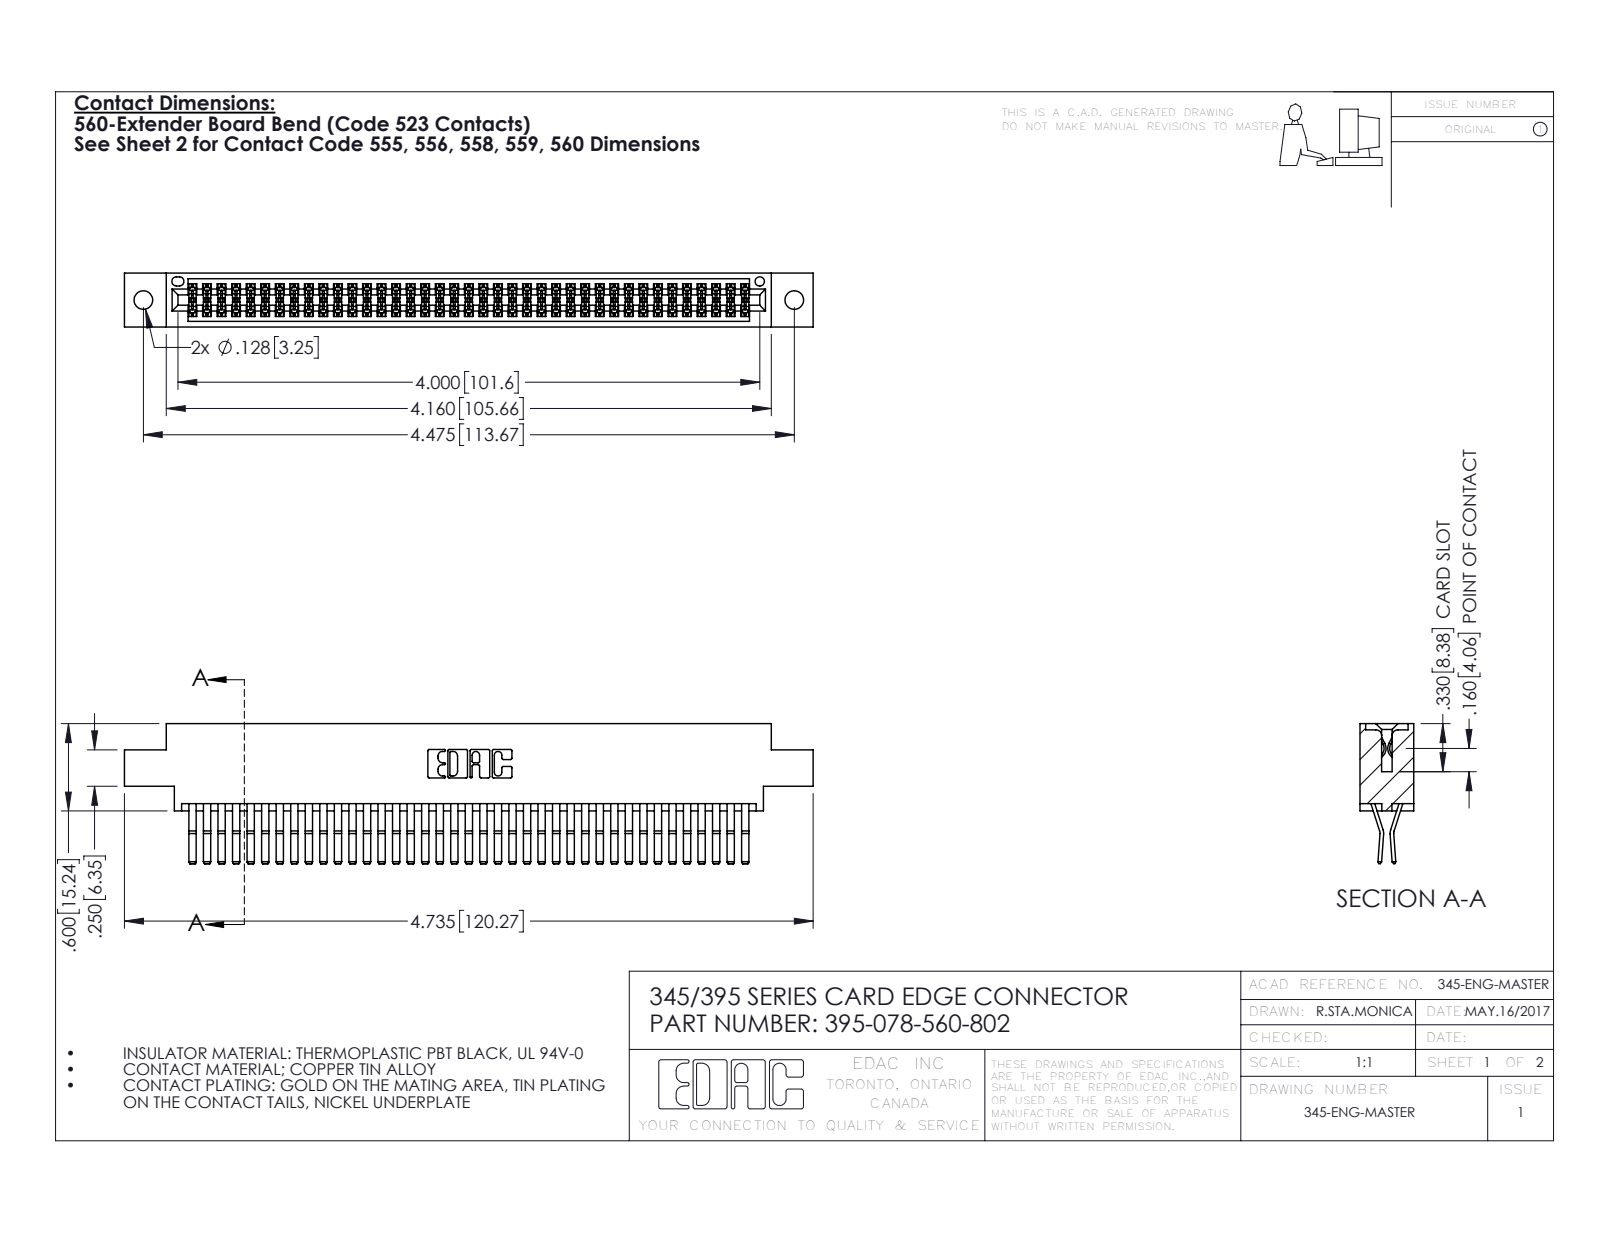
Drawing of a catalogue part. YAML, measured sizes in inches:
part_name: "345-292-001_560 Tail; 345 Part_0.170 Offset - 0.128 Dia; 395-078-560-802"
step_written_by: "SolidWorks 2016 (CONFIG_CONTROL_DESIGN)"
units: inches
bodies: {solids: 79, faces: 4186, planar: 2658, cylindrical: 1528, other: 0}
overall_size: [4.735, 0.962, 0.37]
volume: 0.733
surface_area: 29.28
round_holes:
  - {diameter: 0.128, count: 2}
  - {diameter: 0.064, count: 1}
partial_cylinders:
  - {radius: 0.006, count: 117}
  - {radius: 0.01, count: 22}
  - {radius: 0.007, count: 6}
  - {radius: 0.031, count: 6}
  - {radius: 0.026, count: 3}
  - {radius: 0.01, count: 2}
  - {radius: 0.014, count: 2}
  - {radius: 0.019, count: 2}
face_to_face_distances: [0.025, 0.298, 0.072, 0.37, 0.2, 0.098, 0.272, 0.225, 0.175, 0.149]
hole_center_spacings: [0.27, 4.239, 4.475]
